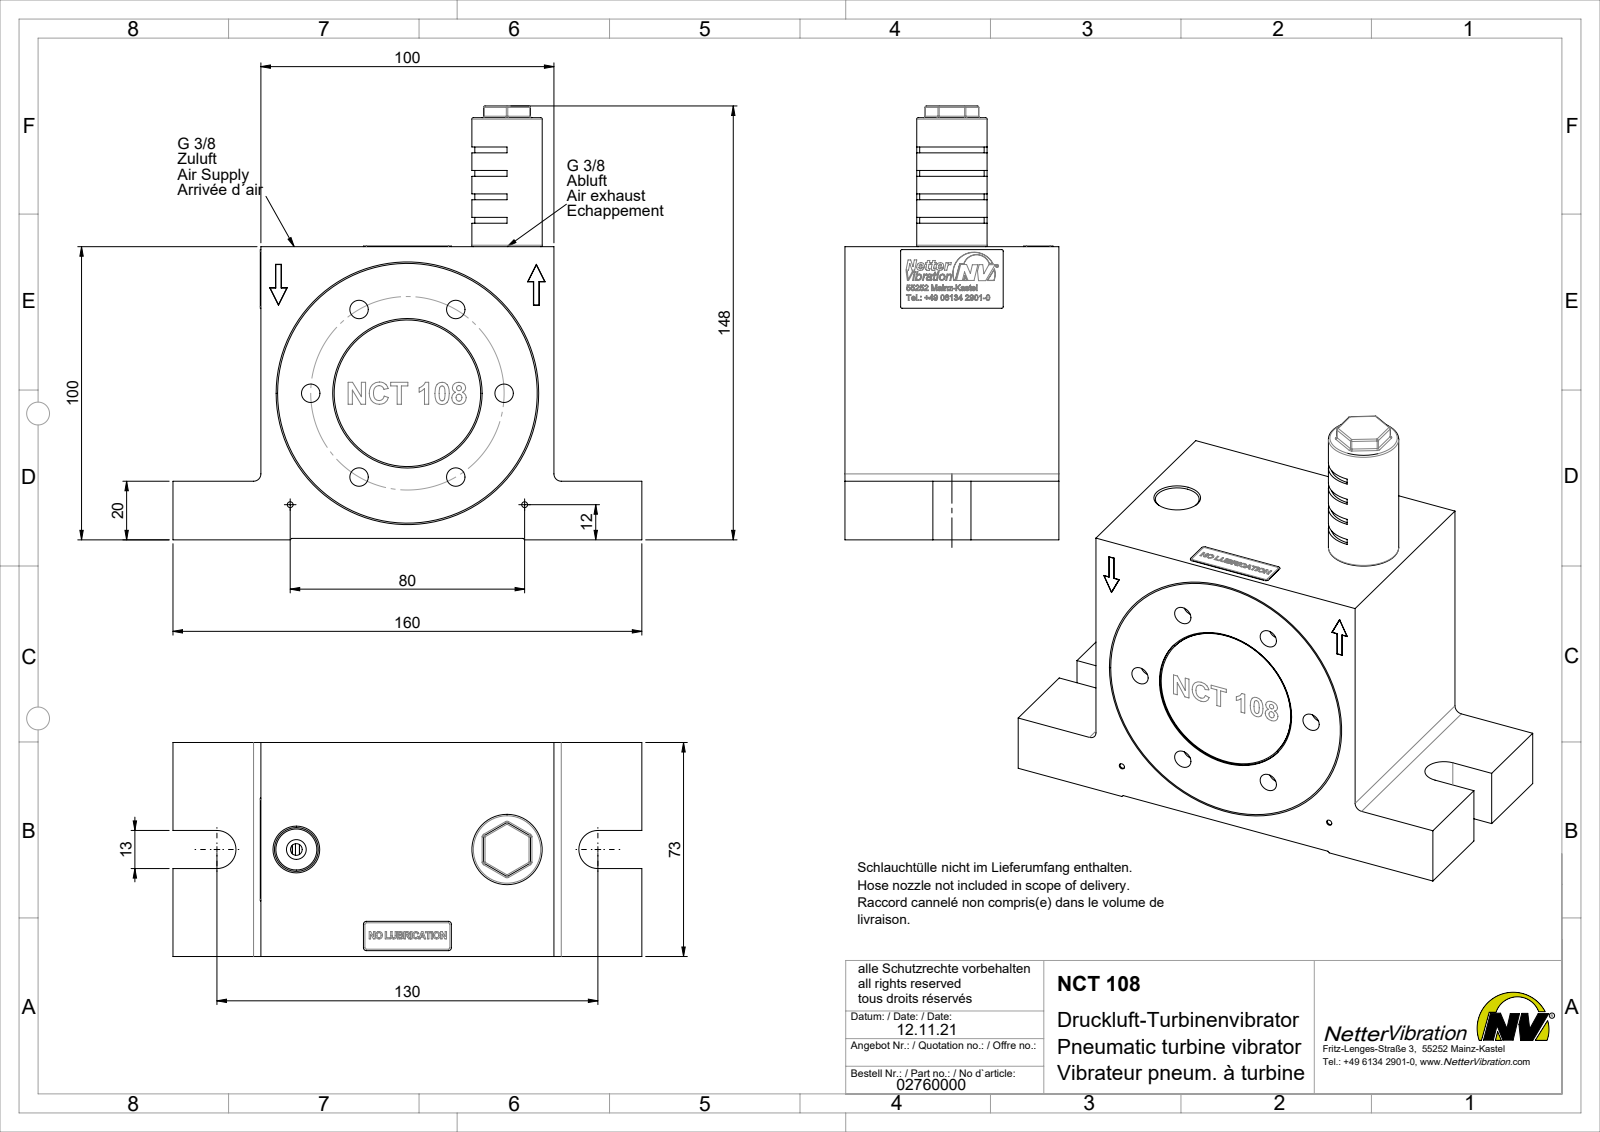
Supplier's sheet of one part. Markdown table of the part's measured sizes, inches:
| quantity | value |
| --- | --- |
| part name | NCT 108 Turbinenvibrator #02760000 |
| STEP written by | SolidWorks 2015 (AUTOMOTIVE_DESIGN) |
| units | inches |
| bodies | 2 solids, 355 faces (213 planar, 81 cylindrical, 61 other) |
| overall size | 6.299 × 5.748 × 2.874 |
| volume | 47.93 in³ |
| surface area | 122.6 in² |
| round holes (diameter × count) | 0.248 × 6, 0.079 × 2, 0.591 × 2, 1.575 × 1, 2.008 × 1, 2.047 × 1, 3.445 × 1, 3.48 × 1 |
| round bosses / shafts (diameter × count) | 3.444 × 1, 3.357 × 1, 1.969 × 1, 0.945 × 1, 0.656 × 1 |
| partial cylindrical surfaces (radius × count) | 0.02 × 22, 0.039 × 4, 0.098 × 2, 0.256 × 2, 0.433 × 1 |
| main face-to-face distances | 3.937, 2.874, 0.02, 3.917, 1.181, 0.787, 0.768, 3.15, 2.126, 0.748 |
| hole center spacings | 1.299, 2.25, 2.598, 0.997, 1.521, 2.172, 2.255, 2.78 |
